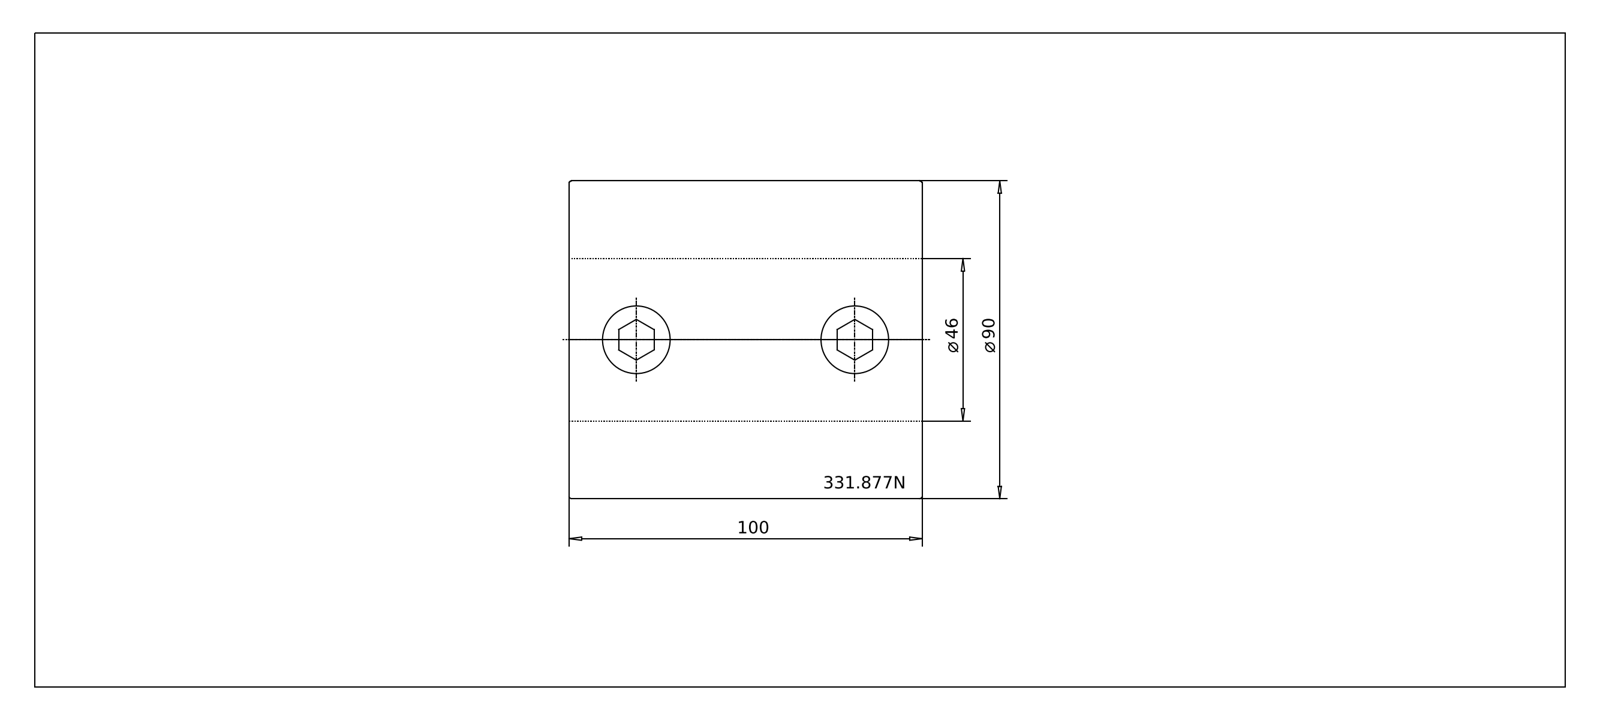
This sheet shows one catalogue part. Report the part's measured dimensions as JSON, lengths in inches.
{"part_name": "331.877N Kaiser R CKN7 X CKN7 X 100 AL|690.437 Kaiser ETL M20 X 29 CK7_Unwucht ;NONE; 331.877N Kaiser R CKN7 X CKN7 X 100 AL|331.877N Kaiser R CKN7 X CKN7 X 100 AL;NONE", "step_written_by": "ACIS (automotive_design)", "units": "inches", "bodies": {"solids": 7, "faces": 238, "planar": 86, "cylindrical": 72, "other": 80}, "overall_size": [3.937, 3.543, 3.543], "volume_in3": 28.65, "surface_area_in2": 109.8, "round_holes": [[0.394, 6], [0.73, 6], [0.817, 6], [0.866, 6], [0.197, 2], [1.811, 1]], "round_bosses_or_shafts": [[0.74, 6], [3.543, 1]], "partial_cylinders_radius": [[1.772, 1]], "face_to_face_distances": [3.937, 0.394, 1.142, 1.219, 0.553, 0.947, 2.99, 3.384, 2.437, 0.825], "hole_center_spacings": [2.437, 0.585, 3.022, 3.606]}
